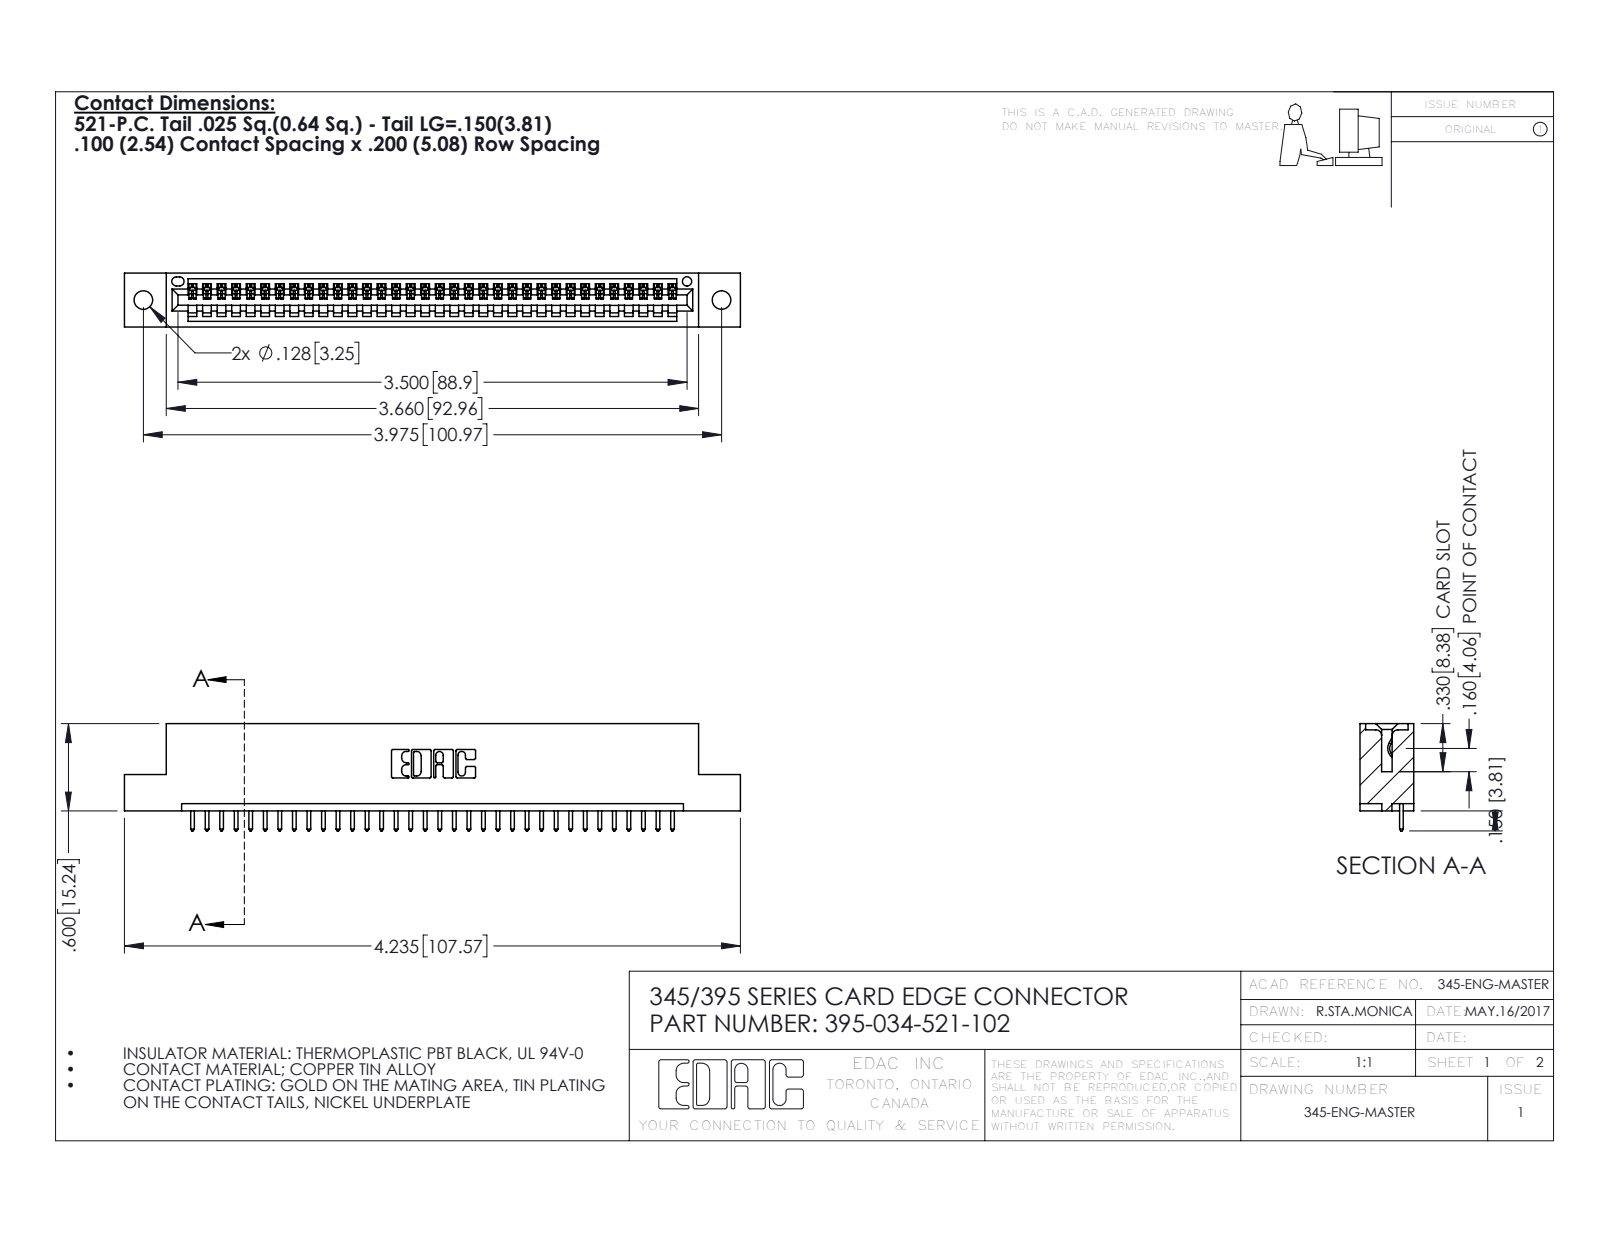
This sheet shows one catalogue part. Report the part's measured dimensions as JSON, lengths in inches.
{"part_name": "345-292-001_345-293-121; 345 Part_Flush Mounting Lugs - 0.128 Dia; 395-034-521-102", "step_written_by": "SolidWorks 2016 (CONFIG_CONTROL_DESIGN)", "units": "inches", "bodies": {"solids": 35, "faces": 2098, "planar": 1440, "cylindrical": 658, "other": 0}, "overall_size": [4.235, 0.737, 0.37], "volume_in3": 0.611, "surface_area_in2": 19.46, "round_holes": [[0.128, 2], [0.064, 1]], "partial_cylinders_radius": [[0.006, 68], [0.01, 68], [0.01, 22], [0.007, 6], [0.031, 6], [0.026, 3], [0.031, 2], [0.04, 2]], "face_to_face_distances": [0.298, 0.072, 0.2, 0.37, 0.098, 0.272, 0.025, 0.225, 0.149, 0.072], "hole_center_spacings": [0.27, 3.74, 3.975]}
